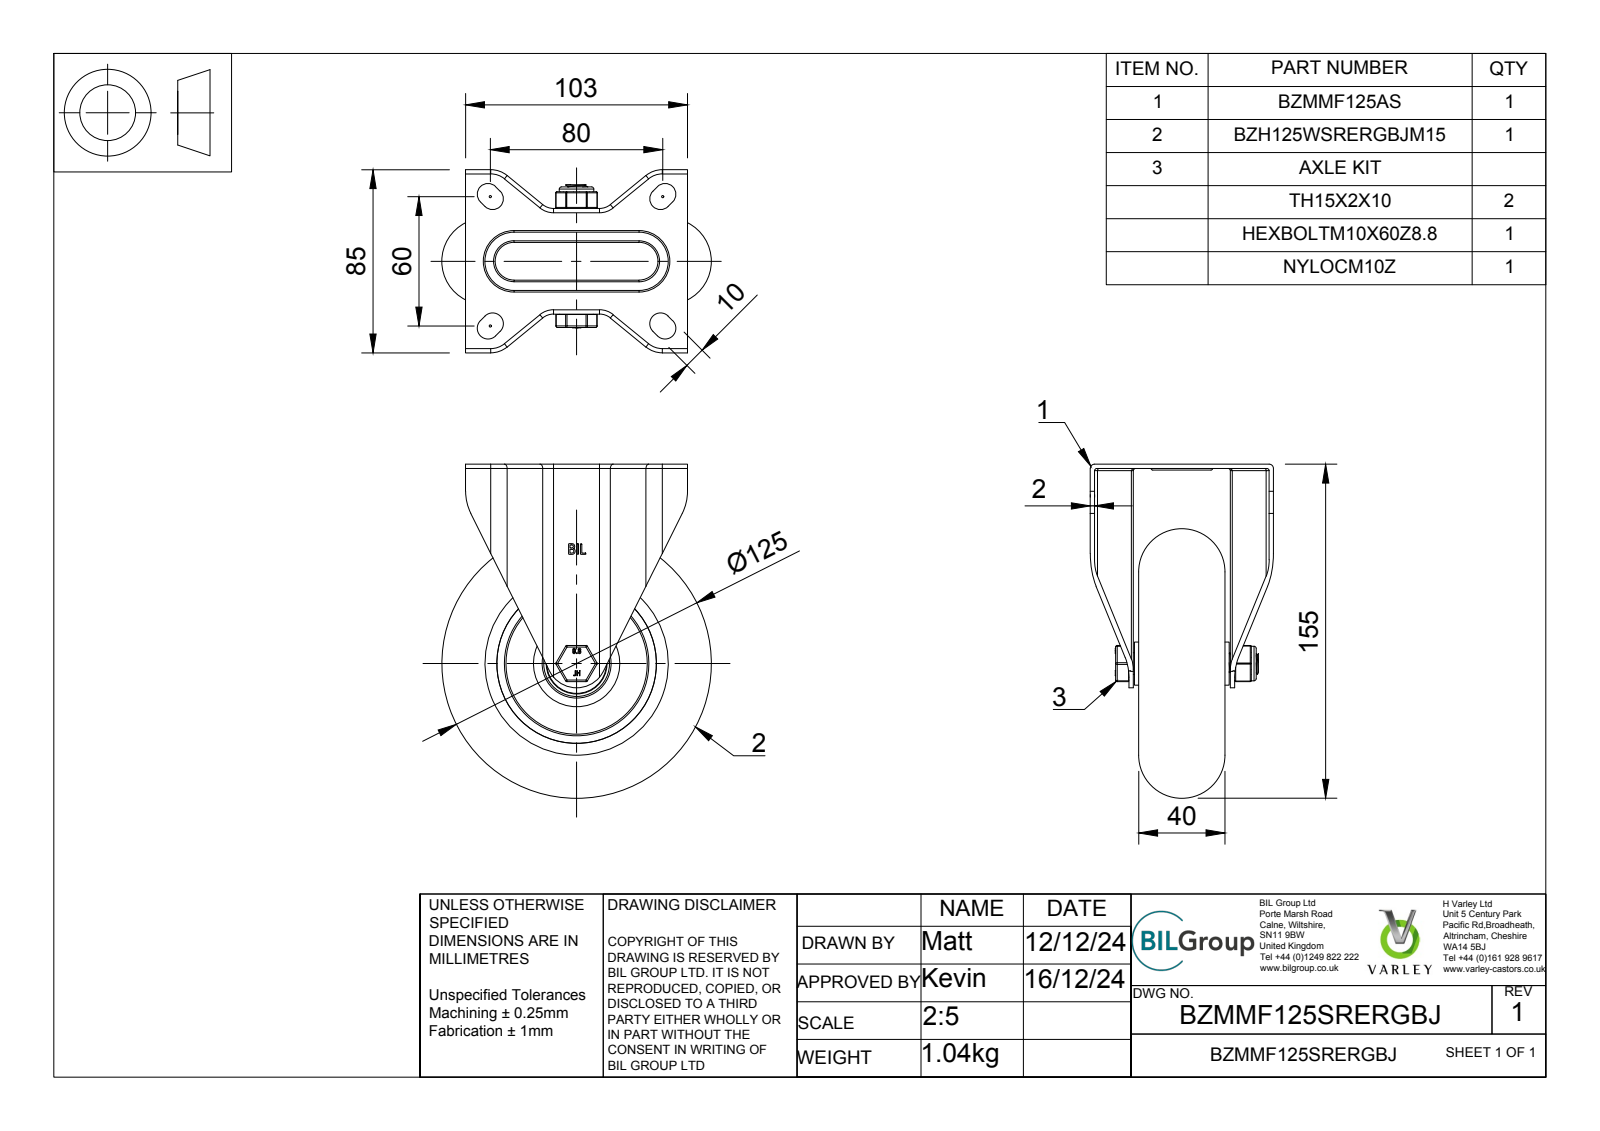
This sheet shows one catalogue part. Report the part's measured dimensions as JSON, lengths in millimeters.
{"part_name": "BZMMF125SRERGBJ v4; BZMMF125AS v1; BZMMF125AS; ZINC PLATED, PRESSED STEEL BRACKET (+8 more)", "step_written_by": "Autodesk Translation Framework v13.20.0.188 (AP242_MANAGED_MODEL_BASED_3D_ENGINEERING_MIM_LF)", "units": "millimeters", "bodies": {"solids": 37, "faces": 1139, "planar": 388, "cylindrical": 223, "other": 528}, "overall_size": [155, 125, 85], "volume_mm3": 397416, "surface_area_mm2": 133944, "round_holes": [[10, 1], [10.2, 1], [10.5, 1], [12, 1], [15, 1], [20.5, 1], [26, 1], [26.8, 1], [28, 1], [28.2, 1], [32, 1], [74, 1]], "round_bosses_or_shafts": [[40, 1], [21.5, 1], [20, 1], [19, 1], [16, 1], [15.5, 1], [14.75, 1], [9.85, 1]], "partial_cylinders_radius": [[0.75, 20], [0.5, 18], [1, 8], [2, 8], [5, 8], [4, 4], [6, 4], [8, 4]], "face_to_face_distances": [2, 18.84, 2.5, 42.5, 44.5, 4.5, 47, 20.25, 28.75, 18.25]}
